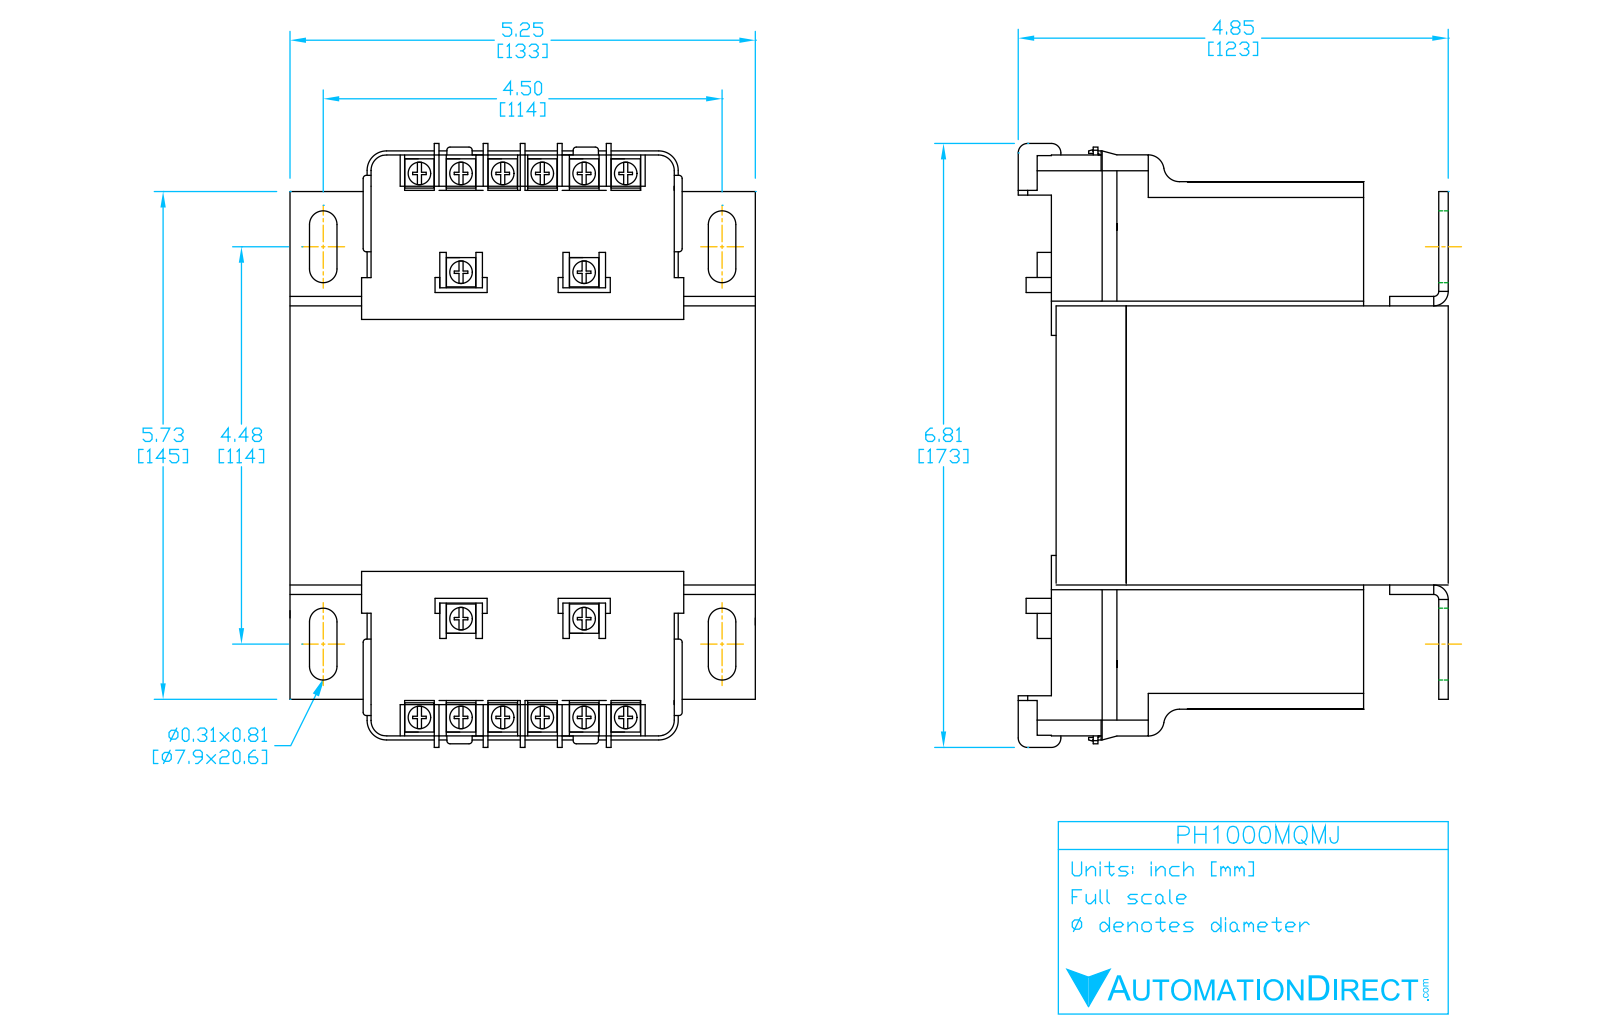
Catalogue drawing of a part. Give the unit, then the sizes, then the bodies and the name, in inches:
Units: inches
Overall size (bounding box): 6.767 × 5.25 × 4.847
Round holes (diameter × count): ⌀0.157 ×4
Partial cylindrical surfaces — rounded edges, fillets, slot ends (radius × count): R0.039 ×102, R0.197 ×10, R0.156 ×8, R0.1 ×4, R0.157 ×4, R0.248 ×4, R0.394 ×4, R0.062 ×2
Main face-to-face distances: 3.15, 3.496, 3.814, 0.318, 4.37, 0.874, 0.556, 0.752, 4.492, 4.847
Hole centre spacings: 3.543, 4.553, 5.769
Volume: 122.2 in³ · Surface area: 333.1 in²
Bodies: 8 solids, 690 faces (386 planar, 220 cylindrical, 84 other)
Part name (STEP PRODUCT): PH1000MQMJ
STEP written by: SolidWorks 2017 (AUTOMOTIVE_DESIGN)
